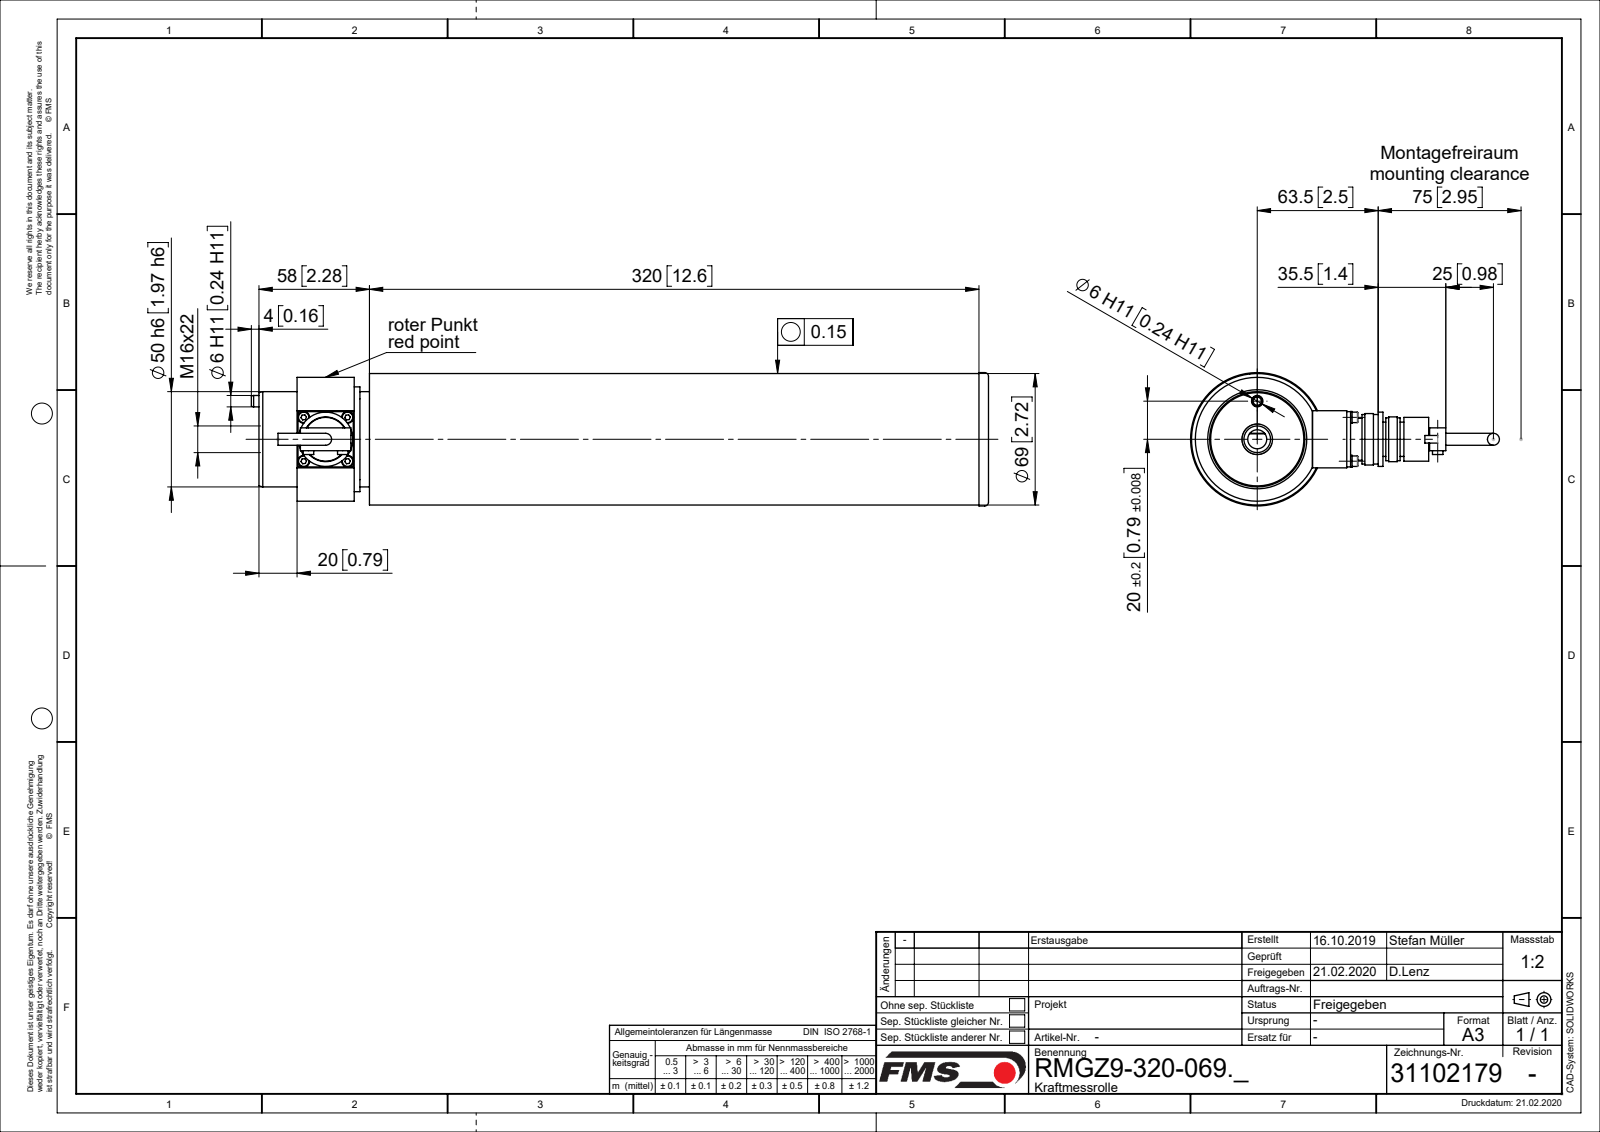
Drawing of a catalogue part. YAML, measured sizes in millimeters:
part_name: "47726-04_stp_01; FLANSCHDOSE_14S-2P_4-POLIG; 49026_01; Spannstift_ISO13337_D06x12 (+8 more)"
step_written_by: "SolidWorks 2018 (CONFIG_CONTROL_DESIGN)"
units: millimeters
bodies: {solids: 31, faces: 597, planar: 172, cylindrical: 259, other: 166}
overall_size: [387, 162.15, 70]
volume: 804072
surface_area: 272746
round_holes:
  - {diameter: 2.5, count: 6}
  - {diameter: 3.1, count: 4}
  - {diameter: 3.4, count: 4}
  - {diameter: 3.3, count: 1}
  - {diameter: 5, count: 1}
  - {diameter: 6, count: 1}
  - {diameter: 10, count: 1}
  - {diameter: 12, count: 1}
  - {diameter: 14, count: 1}
  - {diameter: 17, count: 1}
  - {diameter: 22, count: 1}
  - {diameter: 23, count: 1}
round_bosses_or_shafts:
  - {diameter: 5.5, count: 6}
  - {diameter: 6.2, count: 4}
  - {diameter: 3, count: 4}
  - {diameter: 2.5, count: 4}
  - {diameter: 70, count: 1}
  - {diameter: 69, count: 1}
  - {diameter: 65, count: 1}
  - {diameter: 58, count: 1}
partial_cylinders:
  - {radius: 0.1, count: 4}
  - {radius: 11, count: 4}
  - {radius: 4.19, count: 2}
  - {radius: 4.25, count: 2}
  - {radius: 17.5, count: 1}
  - {radius: 22.2, count: 1}
  - {radius: 25.37, count: 1}
face_to_face_distances: [50, 35, 328, 330, 2, 3, 5, 53, 38, 20]
hole_center_spacings: [16.26, 23, 24.85, 32.53, 18.14, 20, 25.59, 37.16]
